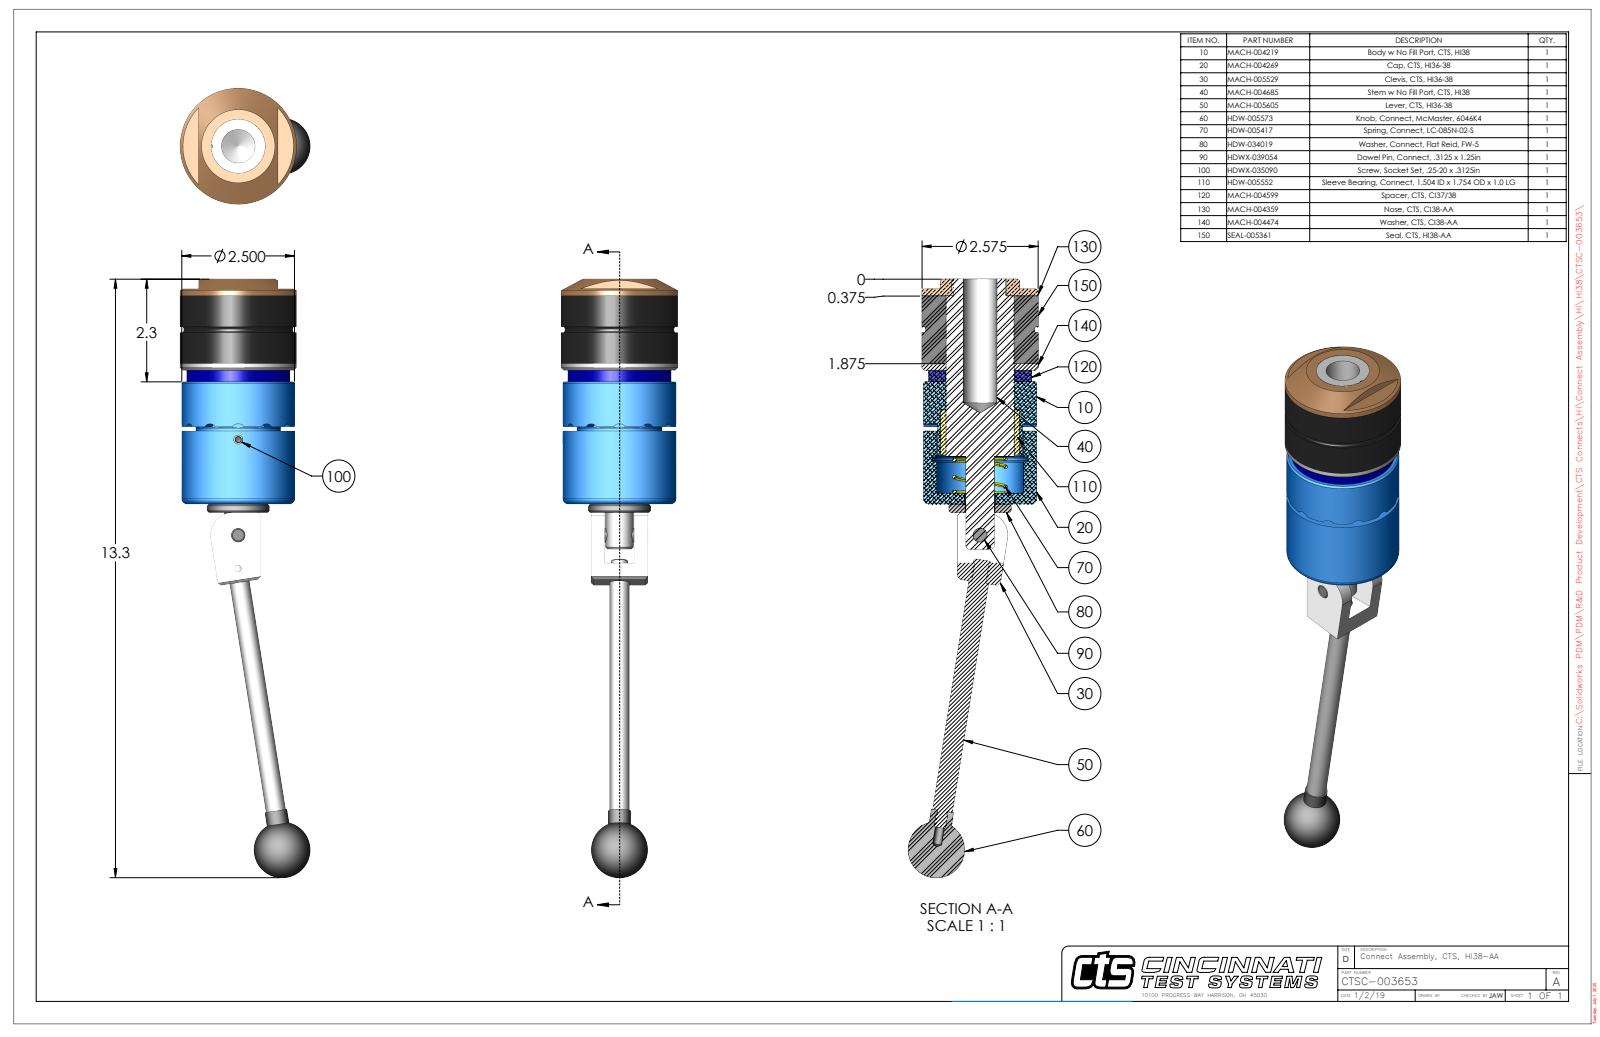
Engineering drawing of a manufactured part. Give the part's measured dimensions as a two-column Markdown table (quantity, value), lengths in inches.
| quantity | value |
| --- | --- |
| part name | CTSC-003653 |
| STEP written by | SolidWorks 2023 (AUTOMOTIVE_DESIGN) |
| units | inches |
| bodies | 10 solids, 335 faces (146 planar, 108 cylindrical, 81 other) |
| overall size | 13.275 × 2.88 × 2.575 |
| volume | 26.41 in³ |
| surface area | 141.6 in² |
| round holes (diameter × count) | 0.201 × 2, 0.15 × 1, 0.311 × 1, 0.313 × 1, 0.314 × 1, 0.656 × 1, 0.696 × 1, 0.75 × 1, 1.172 × 1, 1.495 × 1, 1.501 × 1, 1.51 × 1 |
| round bosses / shafts (diameter × count) | 2.575 × 1, 2.575 × 1, 2.5 × 1, 2.281 × 1, 1.875 × 1, 1.5 × 1, 1.496 × 1, 1.38 × 1 |
| partial cylindrical surfaces (radius × count) | 0.12 × 12, 0.029 × 2, 0.5 × 1, 1.213 × 1 |
| main face-to-face distances | 1.5, 0.152, 1.652, 0.25, 0.402, 1.902, 2.713, 2.963, 3.115, 4.615 |
| hole center spacings | 0.74, 2.118, 2.858 |
